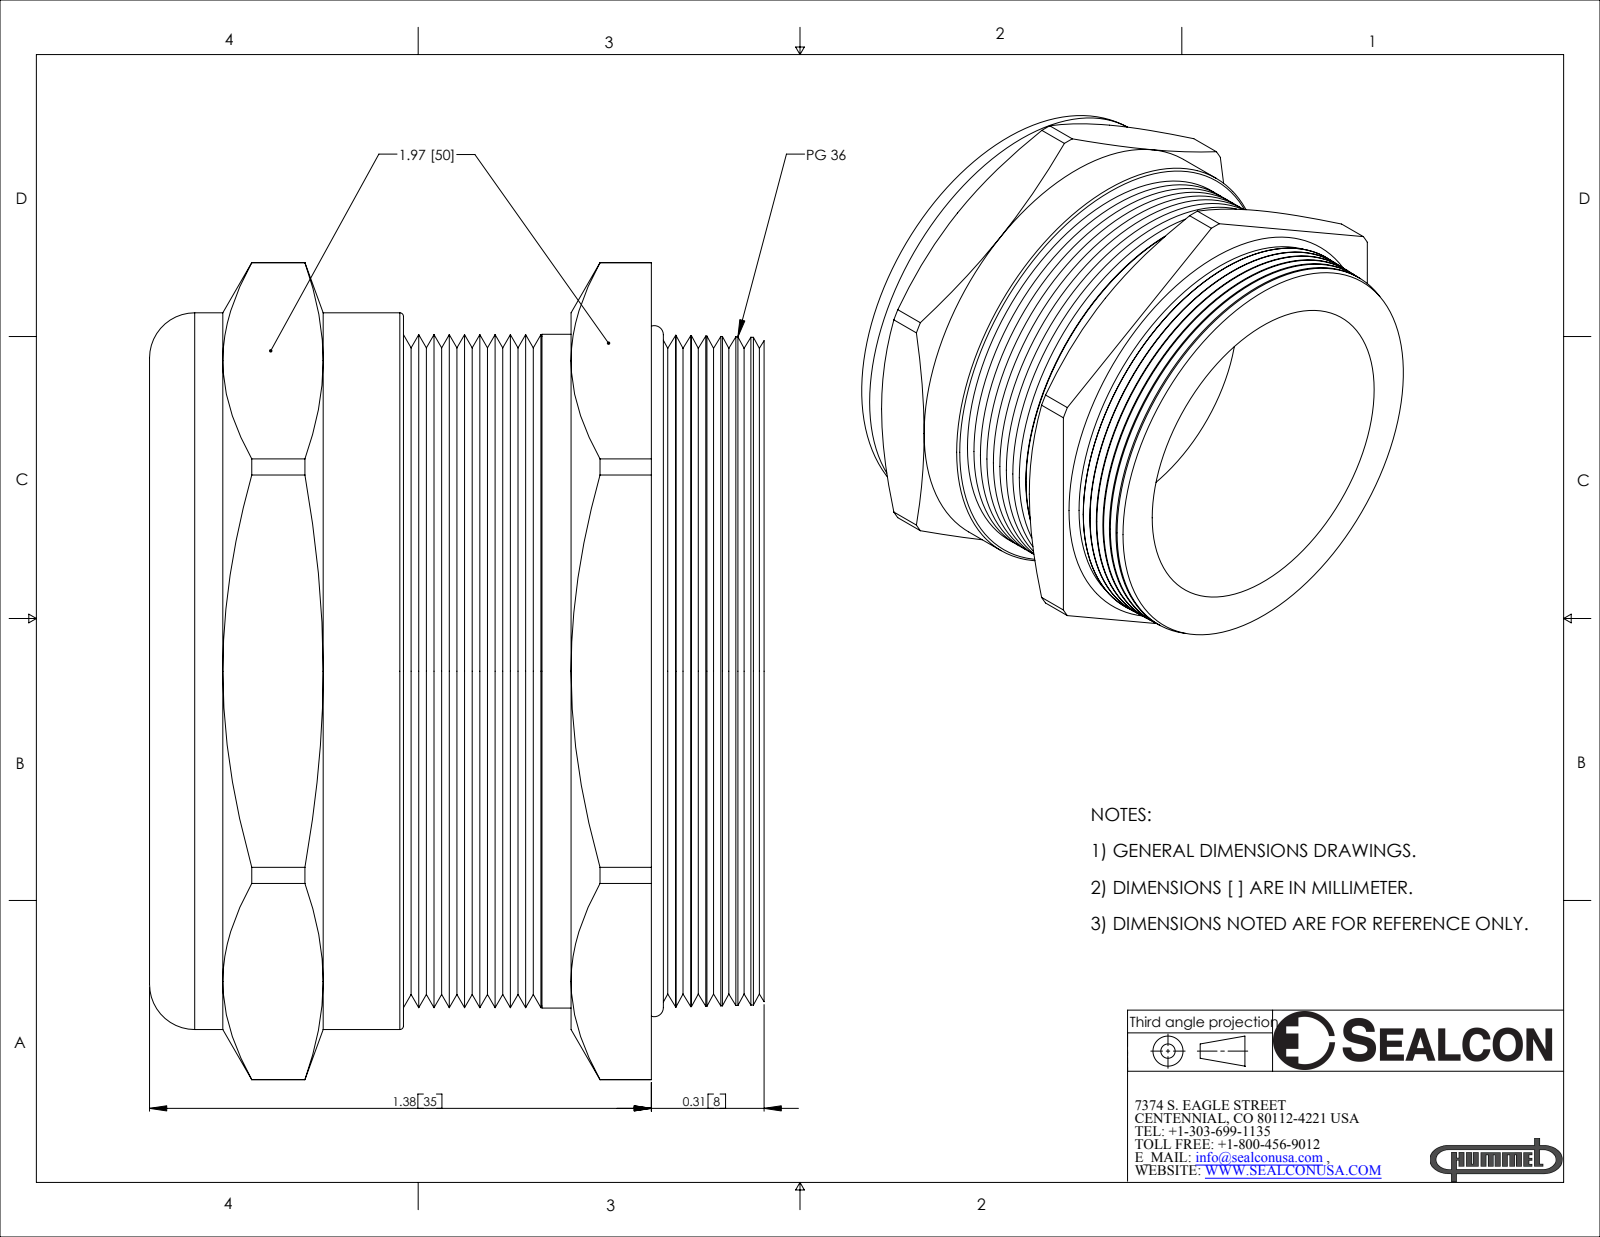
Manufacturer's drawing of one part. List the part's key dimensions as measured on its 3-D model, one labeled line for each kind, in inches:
Part name (STEP PRODUCT): CD36AA-SS
STEP written by: SolidWorks 2007 (CONFIG_CONTROL_DESIGN)
Units: inches
Bodies: 2 solids, 158 faces (22 planar, 28 cylindrical, 108 other)
Overall size (bounding box): 2.246 × 1.97 × 1.69
Volume: 2.416 in³ · Surface area: 27.48 in²
Round holes (diameter × count): ⌀1.35 ×1, ⌀1.428 ×1, ⌀1.85 ×1
Round bosses / shafts (diameter × count): ⌀1.97 ×1, ⌀1.852 ×1
Partial cylindrical surfaces — rounded edges, fillets, slot ends (radius × count): R1.123 ×1
Main face-to-face distances: 1.97, 1.69, 1.38, 0.31, 1.159, 0.221, 0.531, 0.202, 0.957, 1.178
